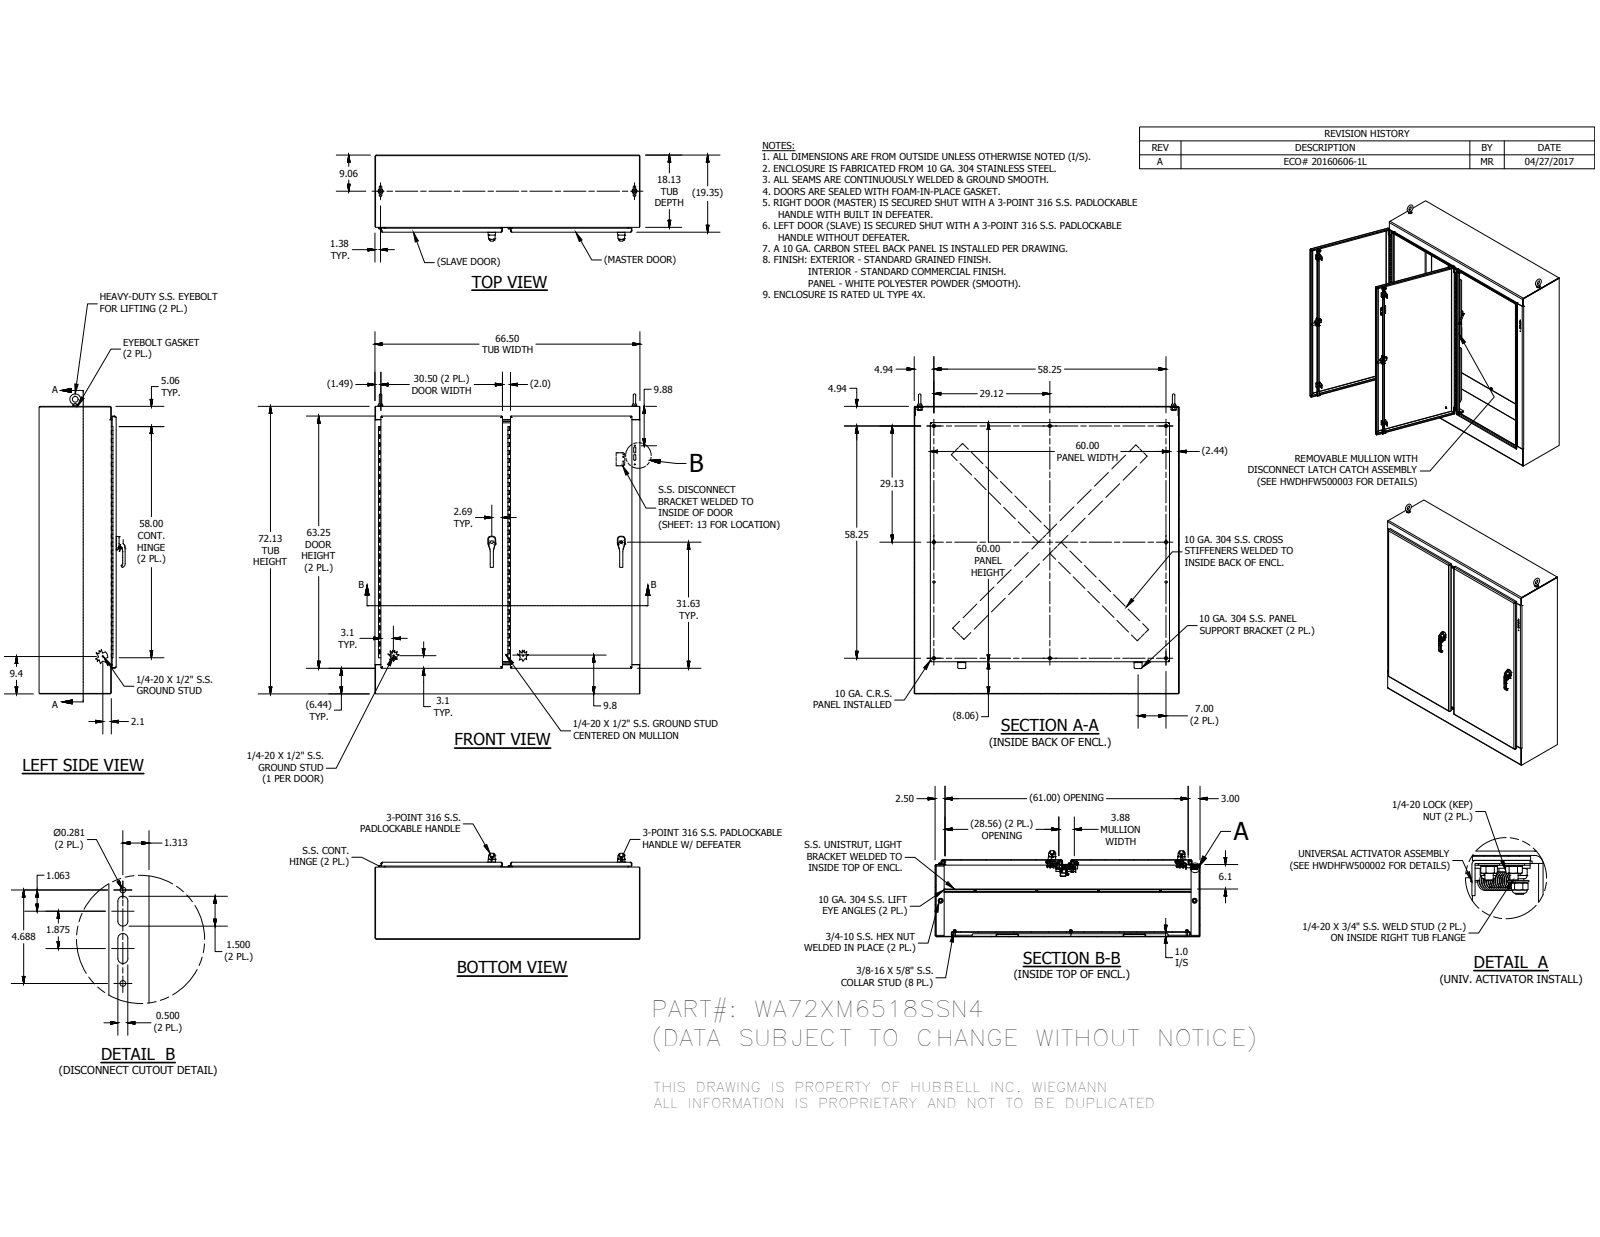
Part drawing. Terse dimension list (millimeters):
name: WA72XM6518SSN4BLS; WAXM6518SSN4TOP; WAXM6518SSN4BTM; HFW332010S (+8 more)
written by: Autodesk Inventor 2016 (AUTOMOTIVE_DESIGN)
unit: mm
bodies: 256 solids, 10672 faces (5046 planar, 3502 cylindrical, 2124 other)
size: 1911.29 × 1689.1 × 548.62
volume: 48 040 000 mm³; area: 28 310 000 mm²
holes: 48× ⌀3.55, 18× ⌀9.52, 17× ⌀6.35, 10× ⌀14.29, 9× ⌀4.76, 8× ⌀3.45, 8× ⌀4.17, 8× ⌀4.83, 8× ⌀4.98, 8× ⌀5.1, 8× ⌀6.65, 8× ⌀7.33
bosses: 18× ⌀8.38, 18× ⌀6.35, 13× ⌀15.88, 12× ⌀8.56, 11× ⌀9.52, 9× ⌀14.29, 8× ⌀7.11, 8× ⌀6.02
rounds: 358× R0.5, 222× R0.3, 192× R0.51, 47× R3.17, 42× R0.47, 36× R1.59, 32× R6.35, 28× R1.27
face distances: 3.4, 3.41, 488.1, 484.7, 25.4, 491.5, 28.8, 462.7, 32.21, 28.81
hole spacings: 0.45, 821.92, 821.7, 821.77, 821.85, 821.99, 821.84, 1377.96
